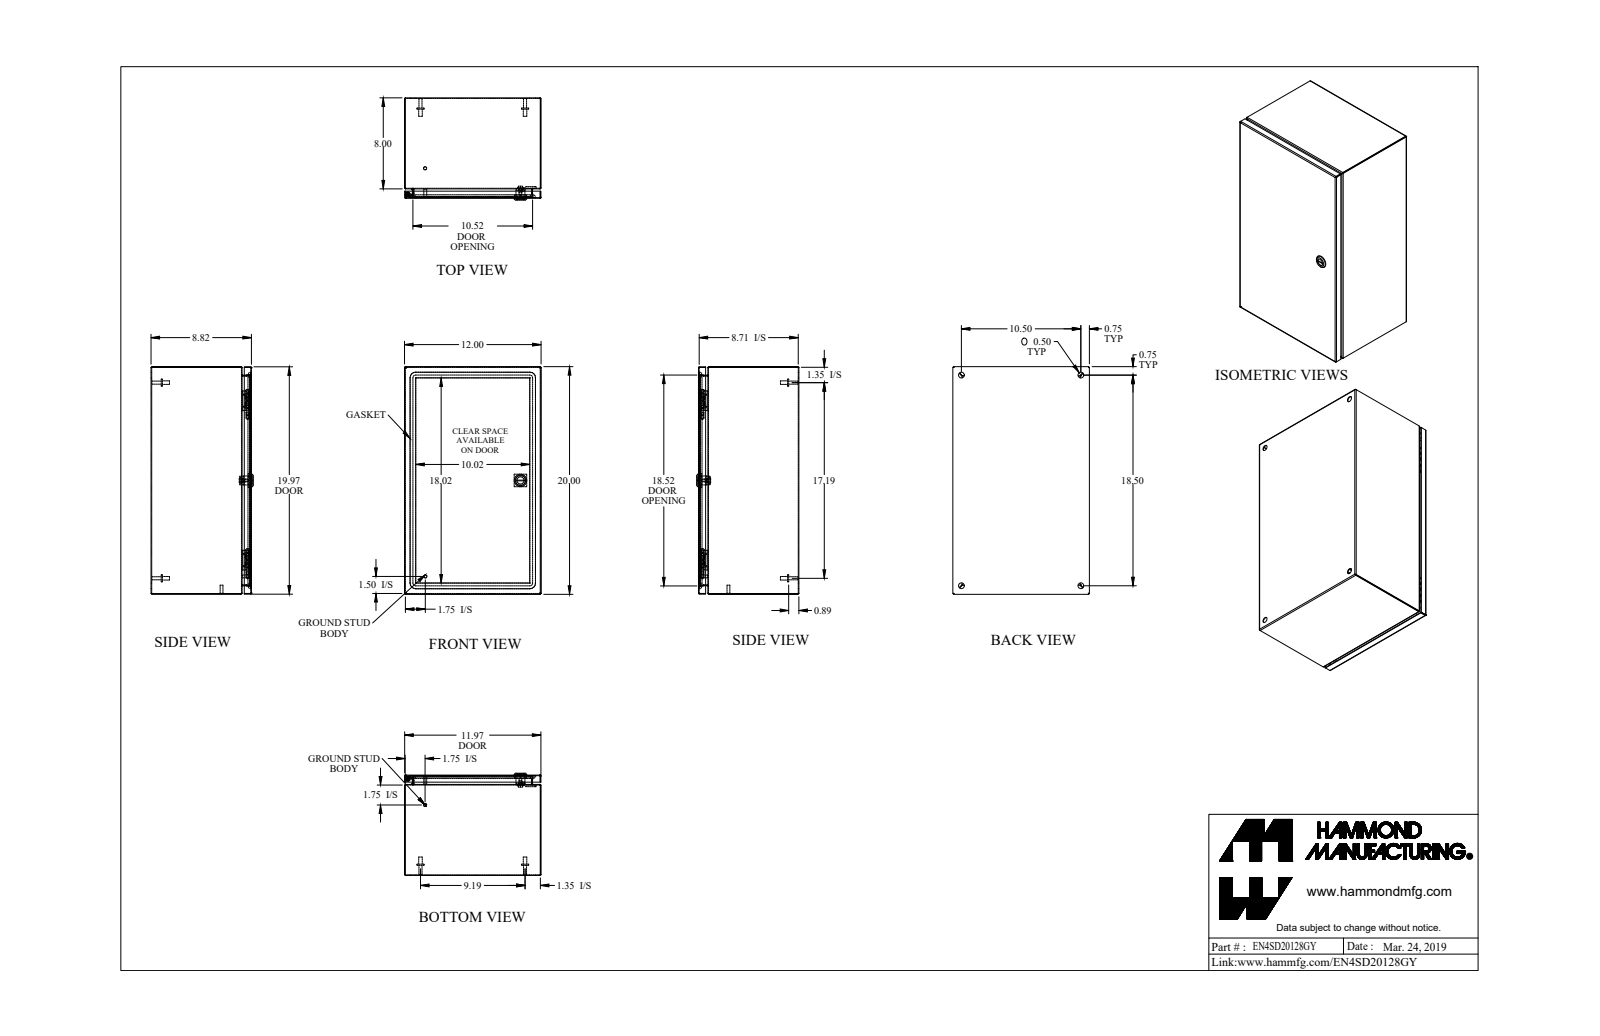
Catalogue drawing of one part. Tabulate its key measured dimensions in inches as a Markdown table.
| quantity | value |
| --- | --- |
| part name | EN4SD20128GY_Default |
| STEP written by | SolidWorks 2019 (CONFIG_CONTROL_DESIGN) |
| units | inches |
| bodies | 21 solids, 634 faces (285 planar, 213 cylindrical, 136 other) |
| overall size | 20 × 12 × 8.982 |
| volume | 70.07 in³ |
| surface area | 2 376 in² |
| round holes (diameter × count) | 0.5 × 4, 0.172 × 1, 0.232 × 1, 0.24 × 1, 0.242 × 1, 0.625 × 1, 0.785 × 1 |
| round bosses / shafts (diameter × count) | 0.625 × 4, 0.313 × 4, 0.27 × 4, 0.281 × 2, 0.25 × 2, 1.1 × 1, 0.525 × 1, 0.455 × 1 |
| partial cylindrical surfaces (radius × count) | 0.029 × 21, 0.086 × 21, 0.25 × 16, 19 × 8, 0.006 × 4, 0.062 × 4, 0.499 × 4, 0.125 × 2 |
| main face-to-face distances | 0.057, 8.765, 11.943, 8.708, 8.822, 19.943, 11.886, 12, 19.886, 20 |
| hole center spacings | 10.5, 18.5, 21.272, 9.31, 9.311, 13.217, 13.217 |
